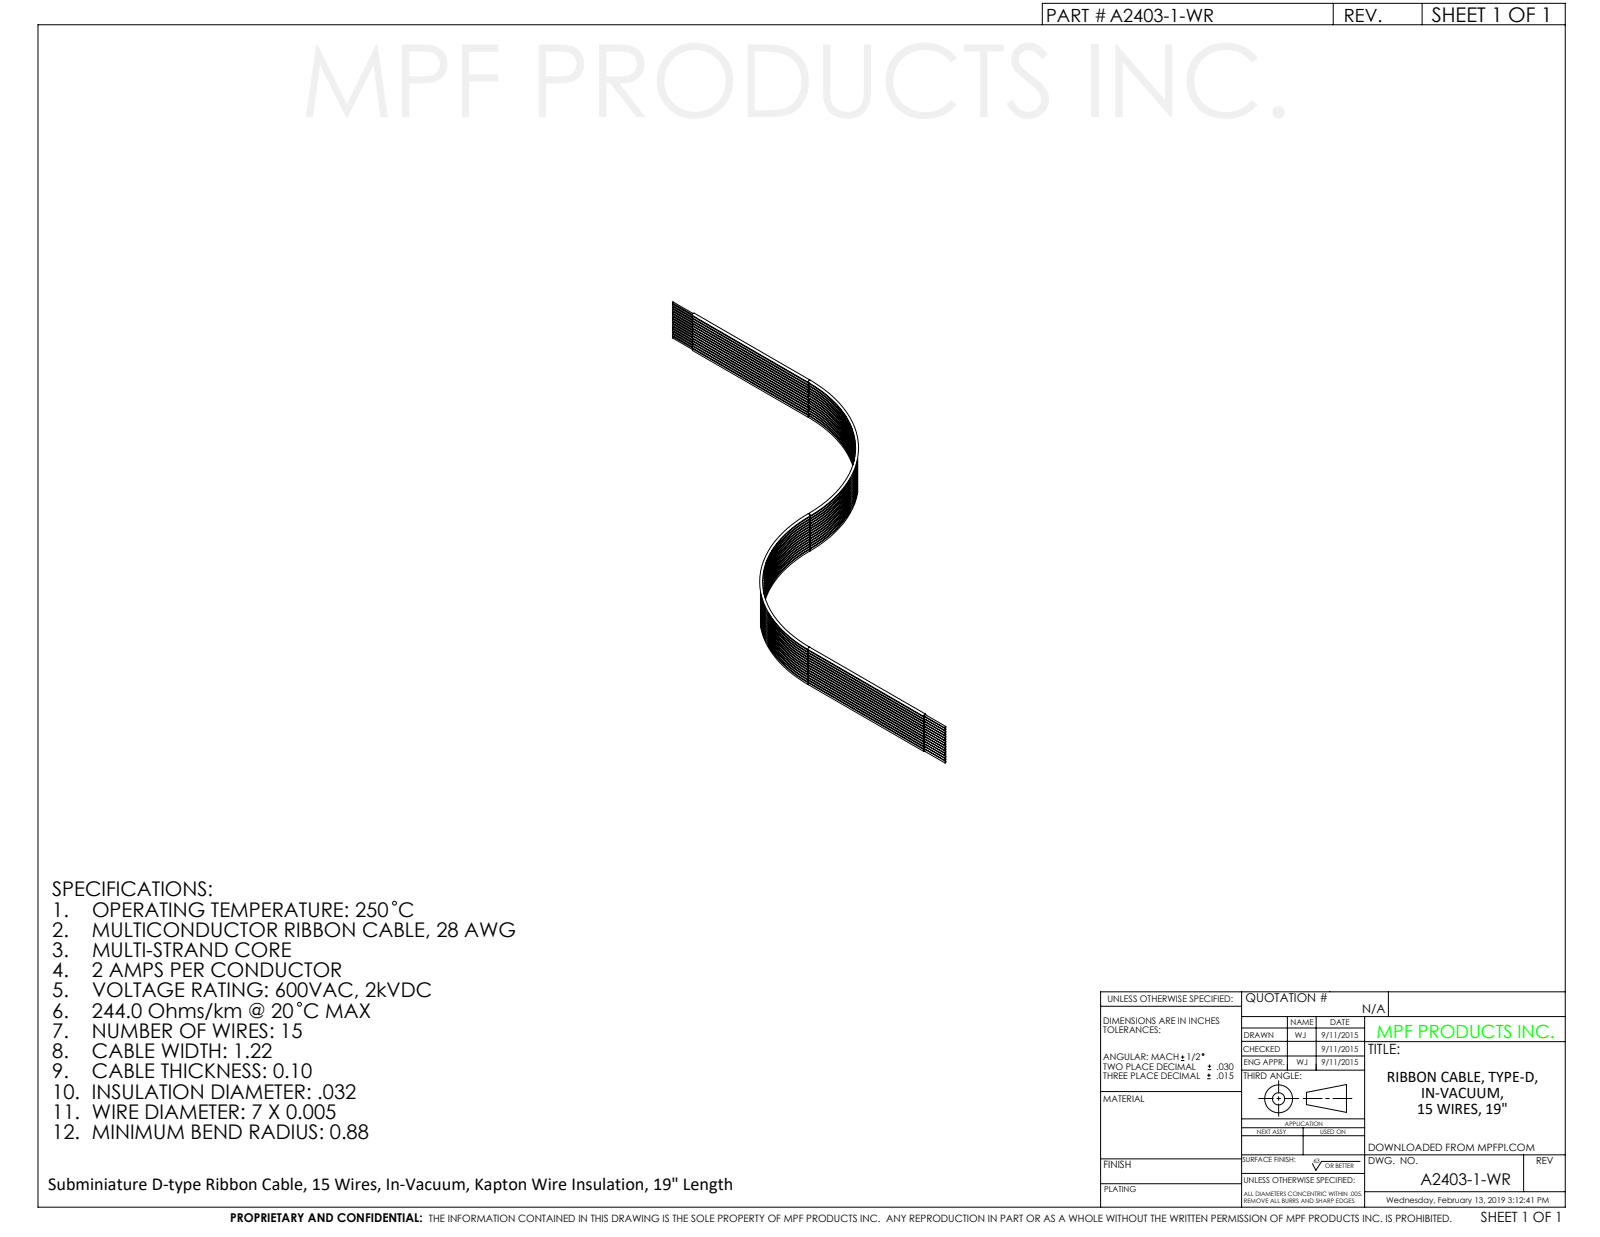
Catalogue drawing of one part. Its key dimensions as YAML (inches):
part_name: "A2403-3-WR"
step_written_by: "SolidWorks 2012 (CONFIG_CONTROL_DESIGN)"
units: inches
bodies: {solids: 1, faces: 409, planar: 116, cylindrical: 203, other: 90}
overall_size: [4.9, 2.27, 0.314]
volume: 0.031
surface_area: 4.289
round_bosses_or_shafts:
  - {diameter: 0.012, count: 15}
  - {diameter: 0.009, count: 15}
partial_cylinders:
  - {radius: 0.01, count: 45}
  - {radius: 1.117, count: 2}
  - {radius: 1.131, count: 2}
face_to_face_distances: [0.013, 2.25, 2.263, 2.237, 4.5, 0.2, 4.7, 4.9, 2.443, 2.457]
